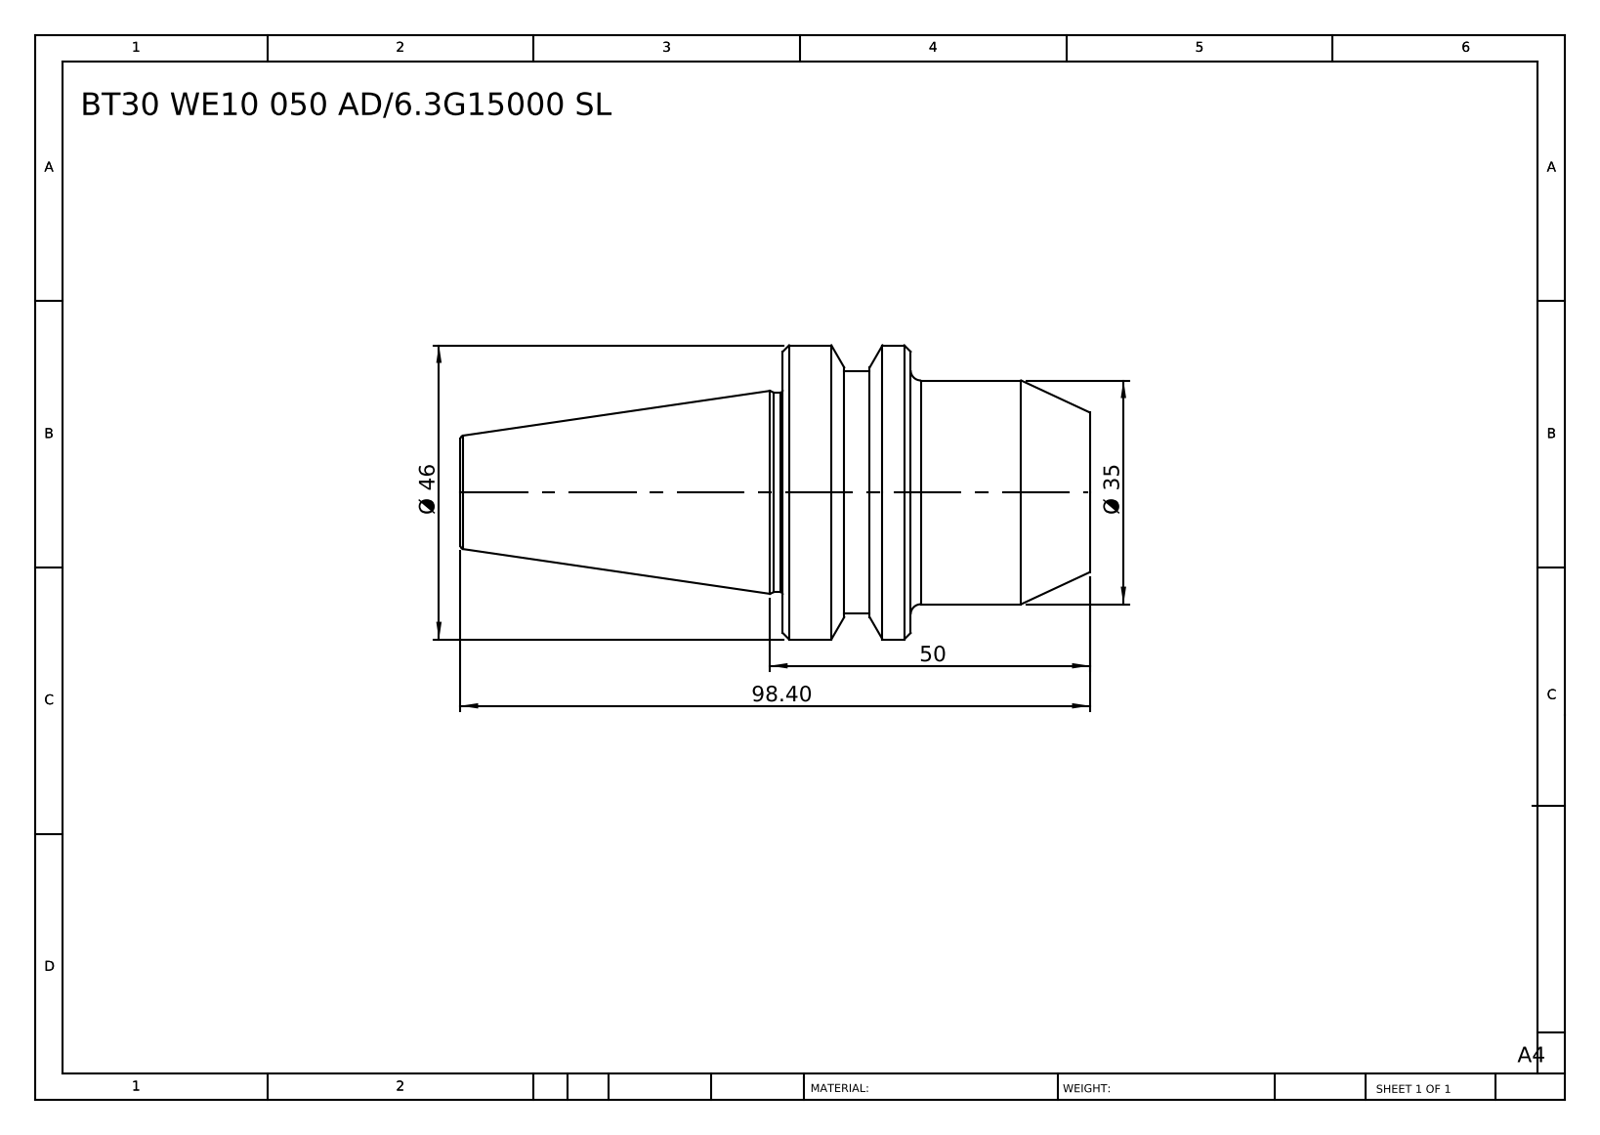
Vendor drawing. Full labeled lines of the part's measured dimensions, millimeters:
Part name (STEP PRODUCT): BT30 WE10 050 AD-6.3G15000 SL
STEP written by: SolidWorks 2014 (CONFIG_CONTROL_DESIGN)
Units: millimetres
Bodies: 1 solid, 36 faces (6 planar, 10 cylindrical, 20 other)
Overall size (bounding box): 98.4 × 46 × 46
Volume: 79 713 mm³ · Surface area: 12 483 mm²
Round bosses / shafts (diameter × count): ⌀46 ×1, ⌀38 ×1, ⌀35 ×1, ⌀31.2 ×1
Main face-to-face distances: 48, 28, 20, 98.4, 70.4, 50.4, 38.4, 10.4, 9.6, 60
